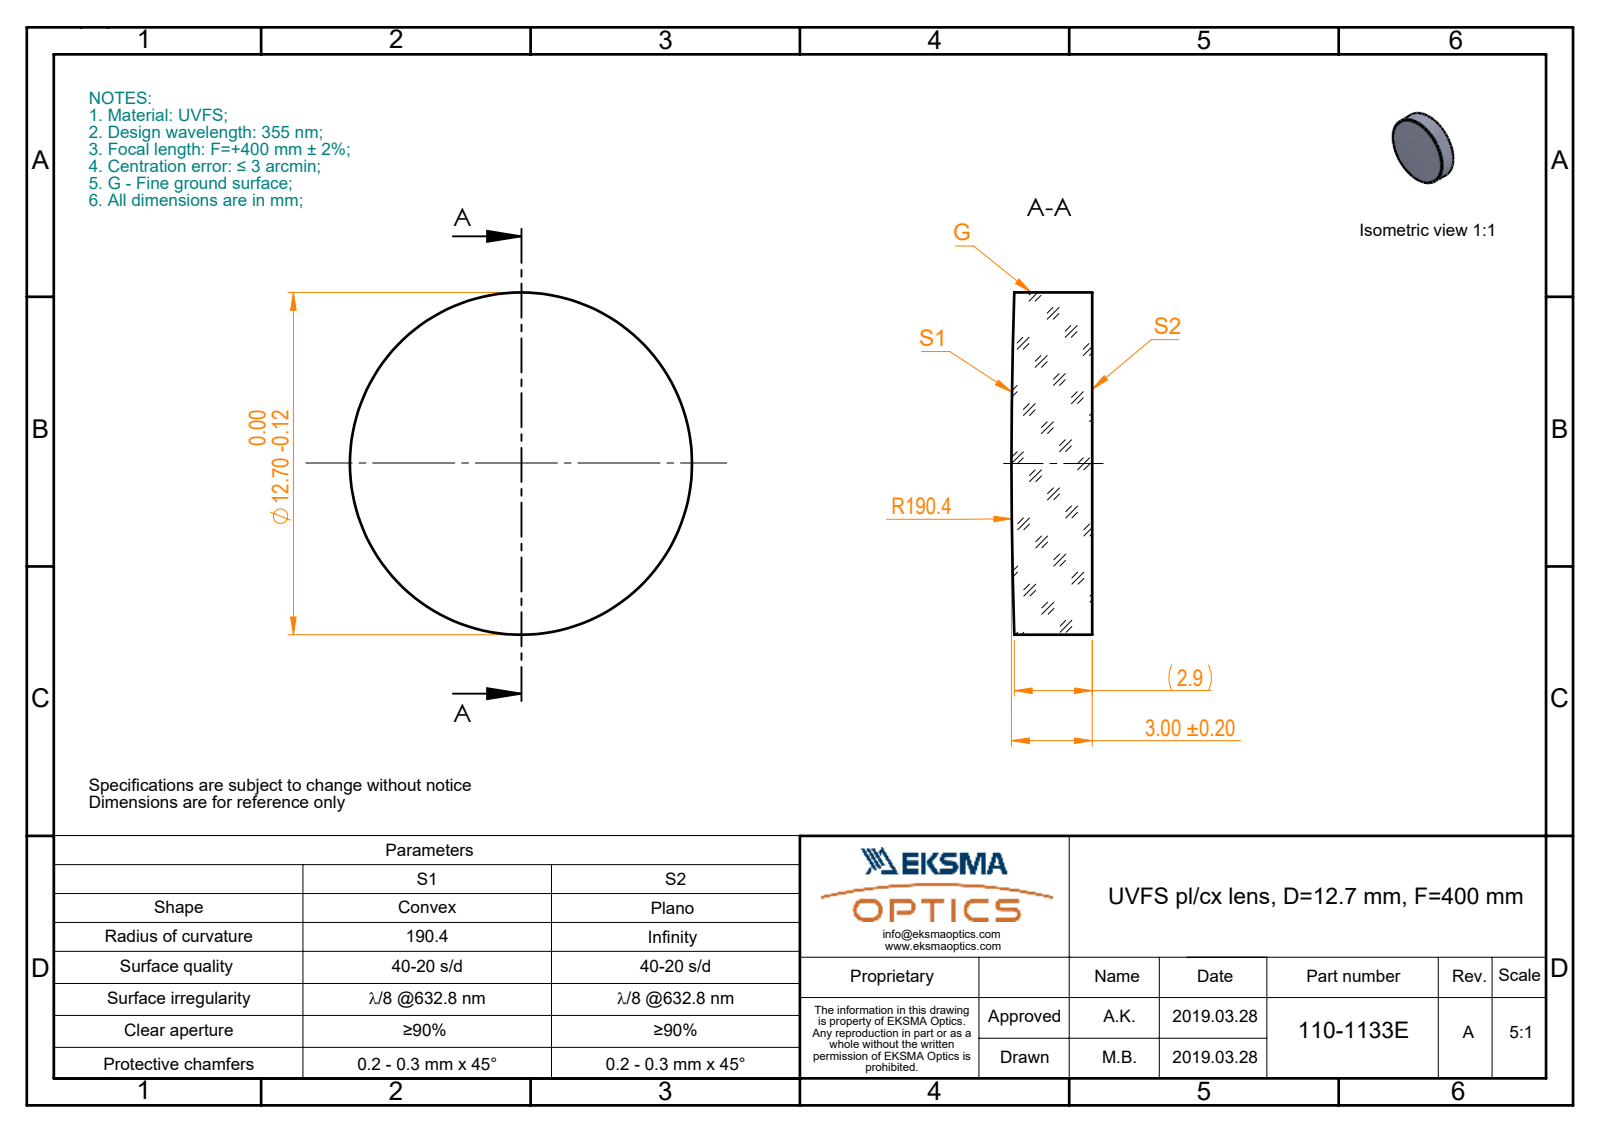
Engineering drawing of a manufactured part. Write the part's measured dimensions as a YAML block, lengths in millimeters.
part_name: "110-1133E UVFS pl-cx 12.7 F400"
step_written_by: "SolidWorks 2017 (CONFIG_CONTROL_DESIGN)"
units: millimeters
bodies: {solids: 1, faces: 5, planar: 1, cylindrical: 2, other: 2}
overall_size: [12.7, 12.7, 3]
volume: 373
surface_area: 369
round_bosses_or_shafts:
  - {diameter: 12.7, count: 1}
